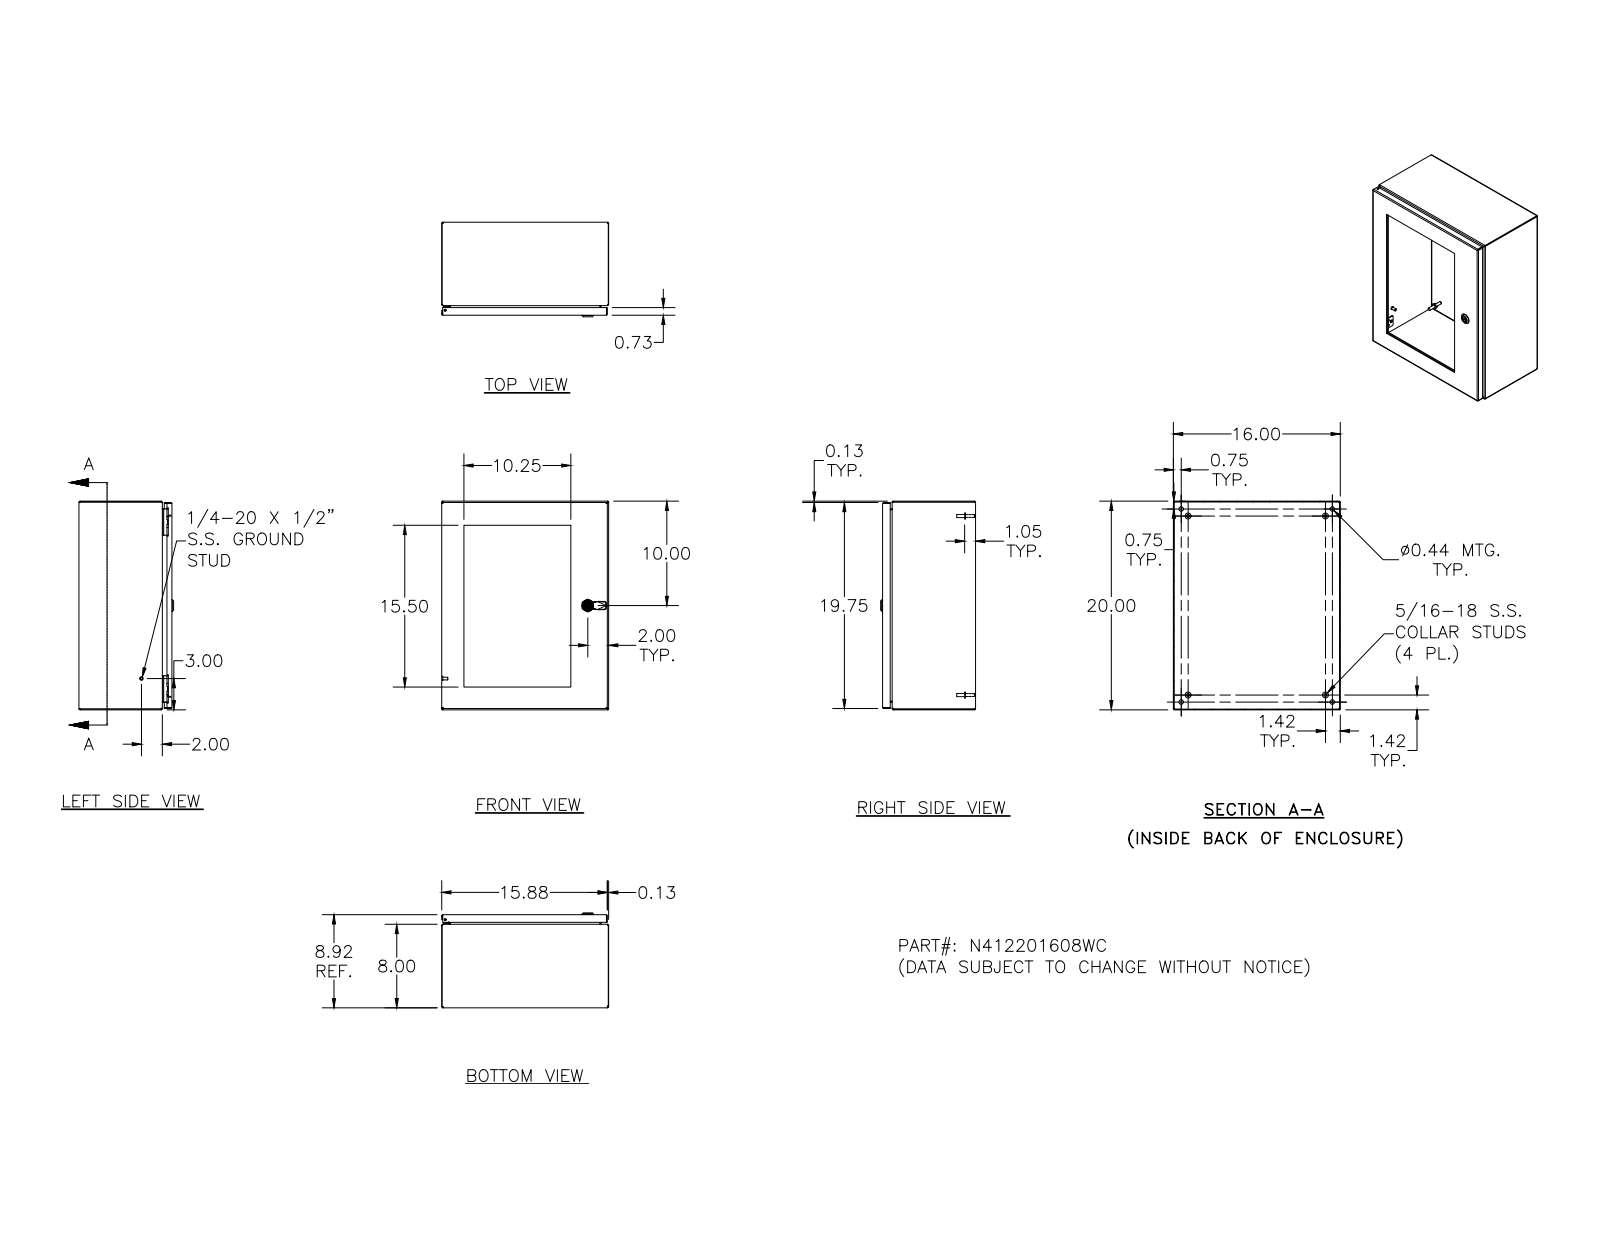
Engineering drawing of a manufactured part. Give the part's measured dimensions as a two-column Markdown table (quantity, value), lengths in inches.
| quantity | value |
| --- | --- |
| part name | N412201608WC |
| STEP written by | SolidWorks 2018 (AUTOMOTIVE_DESIGN) |
| units | inches |
| bodies | 65 solids, 1955 faces (731 planar, 609 cylindrical, 615 other) |
| overall size | 20 × 16 × 9.075 |
| volume | 140.3 in³ |
| surface area | 2 957 in² |
| round holes (diameter × count) | 0.156 × 16, 0.281 × 14, 0.188 × 5, 0.093 × 4, 0.152 × 4, 0.167 × 4, 0.172 × 4, 0.437 × 4, 0.187 × 1, 0.197 × 1, 0.315 × 1, 0.394 × 1 |
| round bosses / shafts (diameter × count) | 0.337 × 14, 0.19 × 14, 0.25 × 10, 0.563 × 4, 0.36 × 4, 0.32 × 4, 0.3 × 4, 0.275 × 4 |
| partial cylindrical surfaces (radius × count) | 0.031 × 34, 0.012 × 30, 0.05 × 26, 0.105 × 24, 0.016 × 18, 0.125 × 16, 0.02 × 13, 0.032 × 8 |
| main face-to-face distances | 0.074, 8.843, 8.769, 15.926, 19.926, 0.25, 8.593, 8.519, 15.852, 16 |
| hole center spacings | 4, 8, 12.176, 16, 6.221, 8.585, 10.035, 11.5 |
